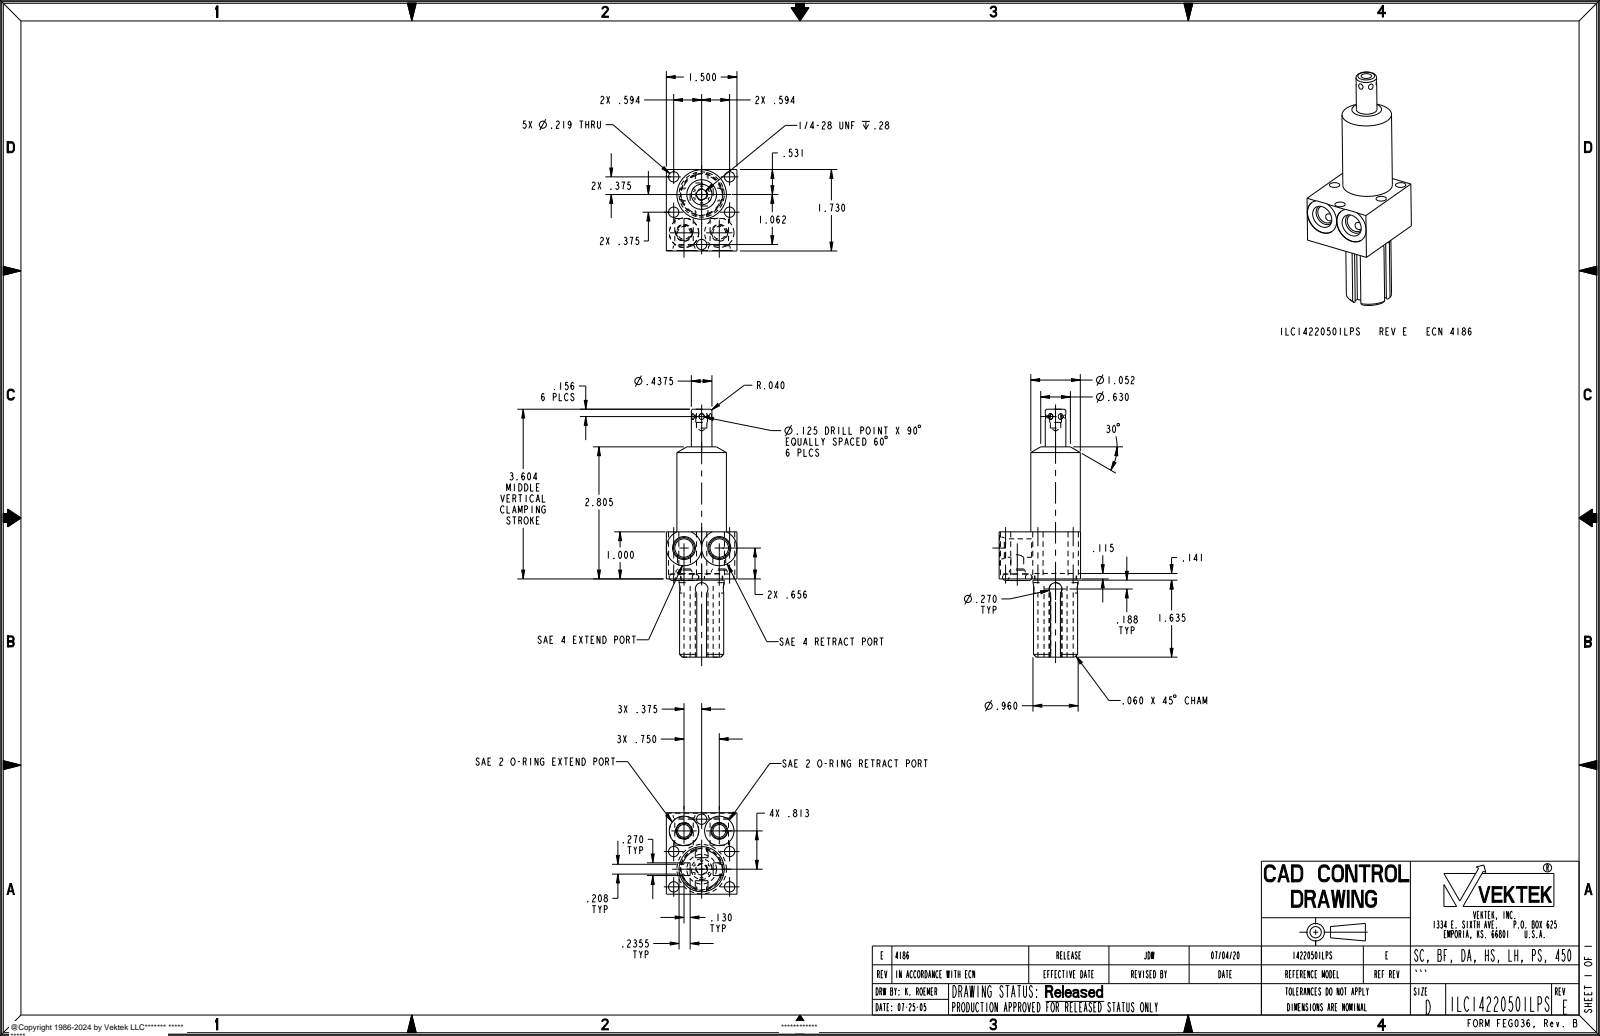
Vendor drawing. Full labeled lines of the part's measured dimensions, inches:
Part name (STEP PRODUCT): ILC14220501LPS
STEP written by: PRO/ENGINEER BY PARAMETRIC TECHNOLOGY CORPORATION, 2013320 (AUTOMOTIVE_DESIGN)
Units: inches
Bodies: 2 solids, 133 faces (49 planar, 42 cylindrical, 42 other)
Overall size (bounding box): 5.265 × 1.73 × 1.5
Volume: 4.606 in³ · Surface area: 34.33 in²
Round holes (diameter × count): ⌀0.219 ×5, ⌀0.272 ×2, ⌀0.392 ×2, ⌀0.625 ×2, ⌀0.75 ×2, ⌀0.221 ×1, ⌀0.895 ×1
Round bosses / shafts (diameter × count): ⌀1.052 ×1, ⌀0.96 ×1, ⌀0.875 ×1, ⌀0.437 ×1, ⌀0.25 ×1
Partial cylindrical surfaces — rounded edges, fillets, slot ends (radius × count): R0.135 ×2
Main face-to-face distances: 1.5, 0.109, 0.38, 1, 0.141, 0.348, 0.031, 0.239, 0.506, 0.994
Hole centre spacings: 0.702, 0.75, 0.45, 0.49, 0.895, 0.908, 1.063, 1.188
